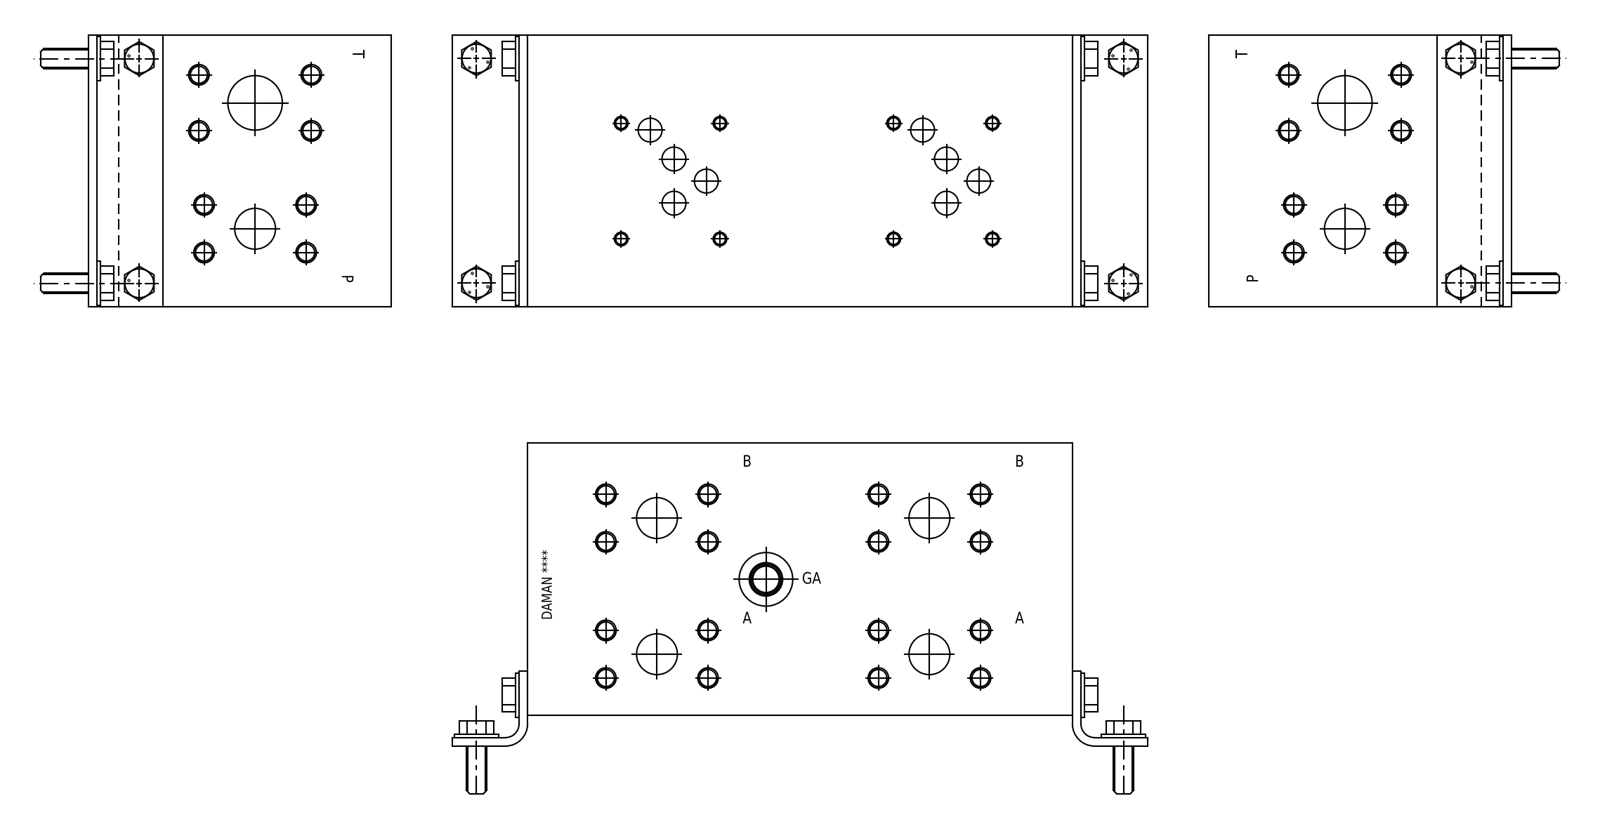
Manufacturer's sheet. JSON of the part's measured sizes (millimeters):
{"part_name": "D05HP025F", "step_written_by": "Autodesk Inventor 2021 (AUTOMOTIVE_DESIGN)", "units": "millimeters", "bodies": {"solids": 1, "faces": 702, "planar": 386, "cylindrical": 109, "other": 207}, "overall_size": [254, 127, 127], "volume_mm3": 3990000, "surface_area_mm2": 200995, "round_holes": [[7.92, 26], [9.53, 26], [5.11, 8], [6.35, 8], [11.13, 8], [19.05, 5], [12.29, 1], [12.9, 1], [14.27, 1], [14.53, 1], [25.02, 1], [25.4, 1]], "face_to_face_distances": [127, 254, 25.4, 228.6, 101.6, 0.79, 24.61, 126.21, 25.36, 0.75], "hole_center_spacings": [127, 26.26, 22.19, 141.99, 78.3, 26.25, 47.59, 52.51]}
